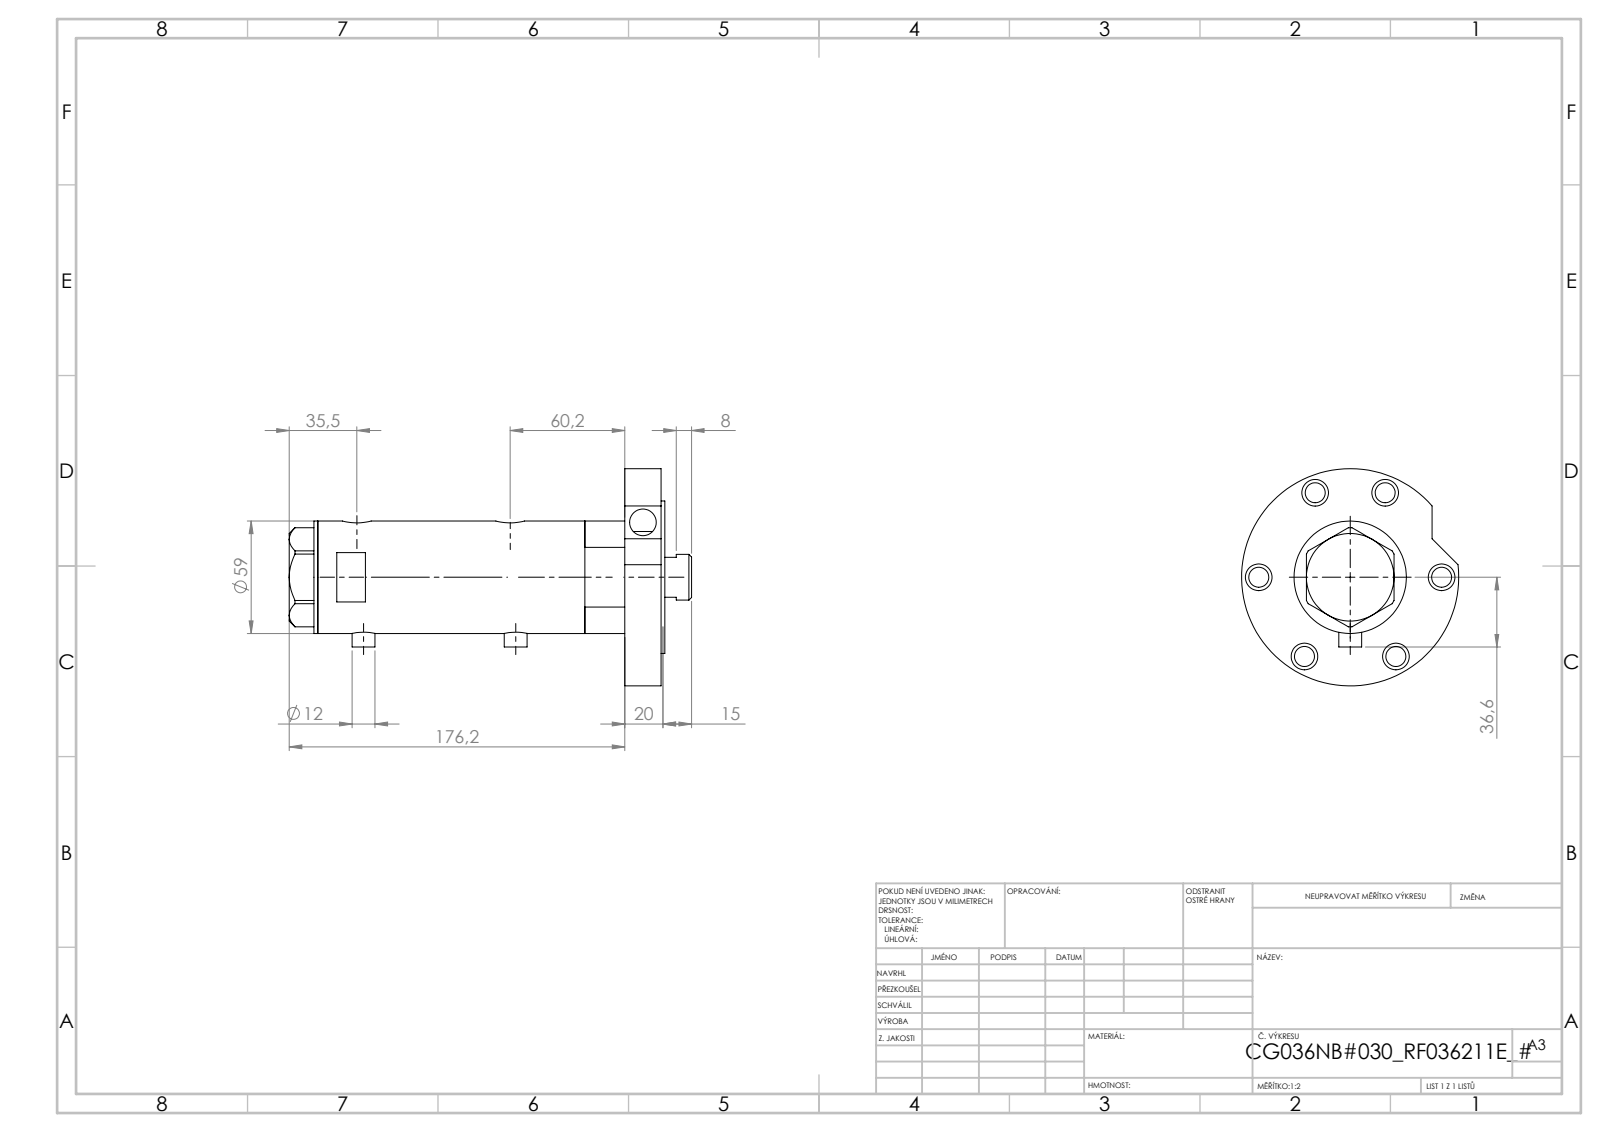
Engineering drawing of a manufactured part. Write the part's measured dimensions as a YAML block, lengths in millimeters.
part_name: "V270CG_FRONT; V270CG_MIDDLE; V270CG_VC; V270CG_BACK (+1 more)"
step_written_by: "SolidWorks 2019 (CONFIG_CONTROL_DESIGN)"
units: millimeters
bodies: {solids: 5, faces: 164, planar: 62, cylindrical: 82, other: 20}
overall_size: [211.2, 114, 114]
volume: 625166
surface_area: 134138
round_holes:
  - {diameter: 14, count: 7}
  - {diameter: 10.5, count: 6}
  - {diameter: 9.73, count: 2}
  - {diameter: 12.5, count: 2}
  - {diameter: 15, count: 2}
  - {diameter: 8.5, count: 1}
  - {diameter: 25, count: 1}
  - {diameter: 26.5, count: 1}
  - {diameter: 36, count: 1}
  - {diameter: 40, count: 1}
  - {diameter: 48, count: 1}
  - {diameter: 52, count: 1}
round_bosses_or_shafts:
  - {diameter: 12, count: 2}
  - {diameter: 114, count: 1}
  - {diameter: 80, count: 1}
  - {diameter: 59, count: 1}
  - {diameter: 46, count: 1}
  - {diameter: 24, count: 1}
face_to_face_distances: [2, 19, 21, 182.2, 161.2, 180.2, 102.2, 59, 78, 80]
hole_center_spacings: [48, 53.34, 79.82, 83.14, 86.1, 95.8, 2.9, 3.5]
